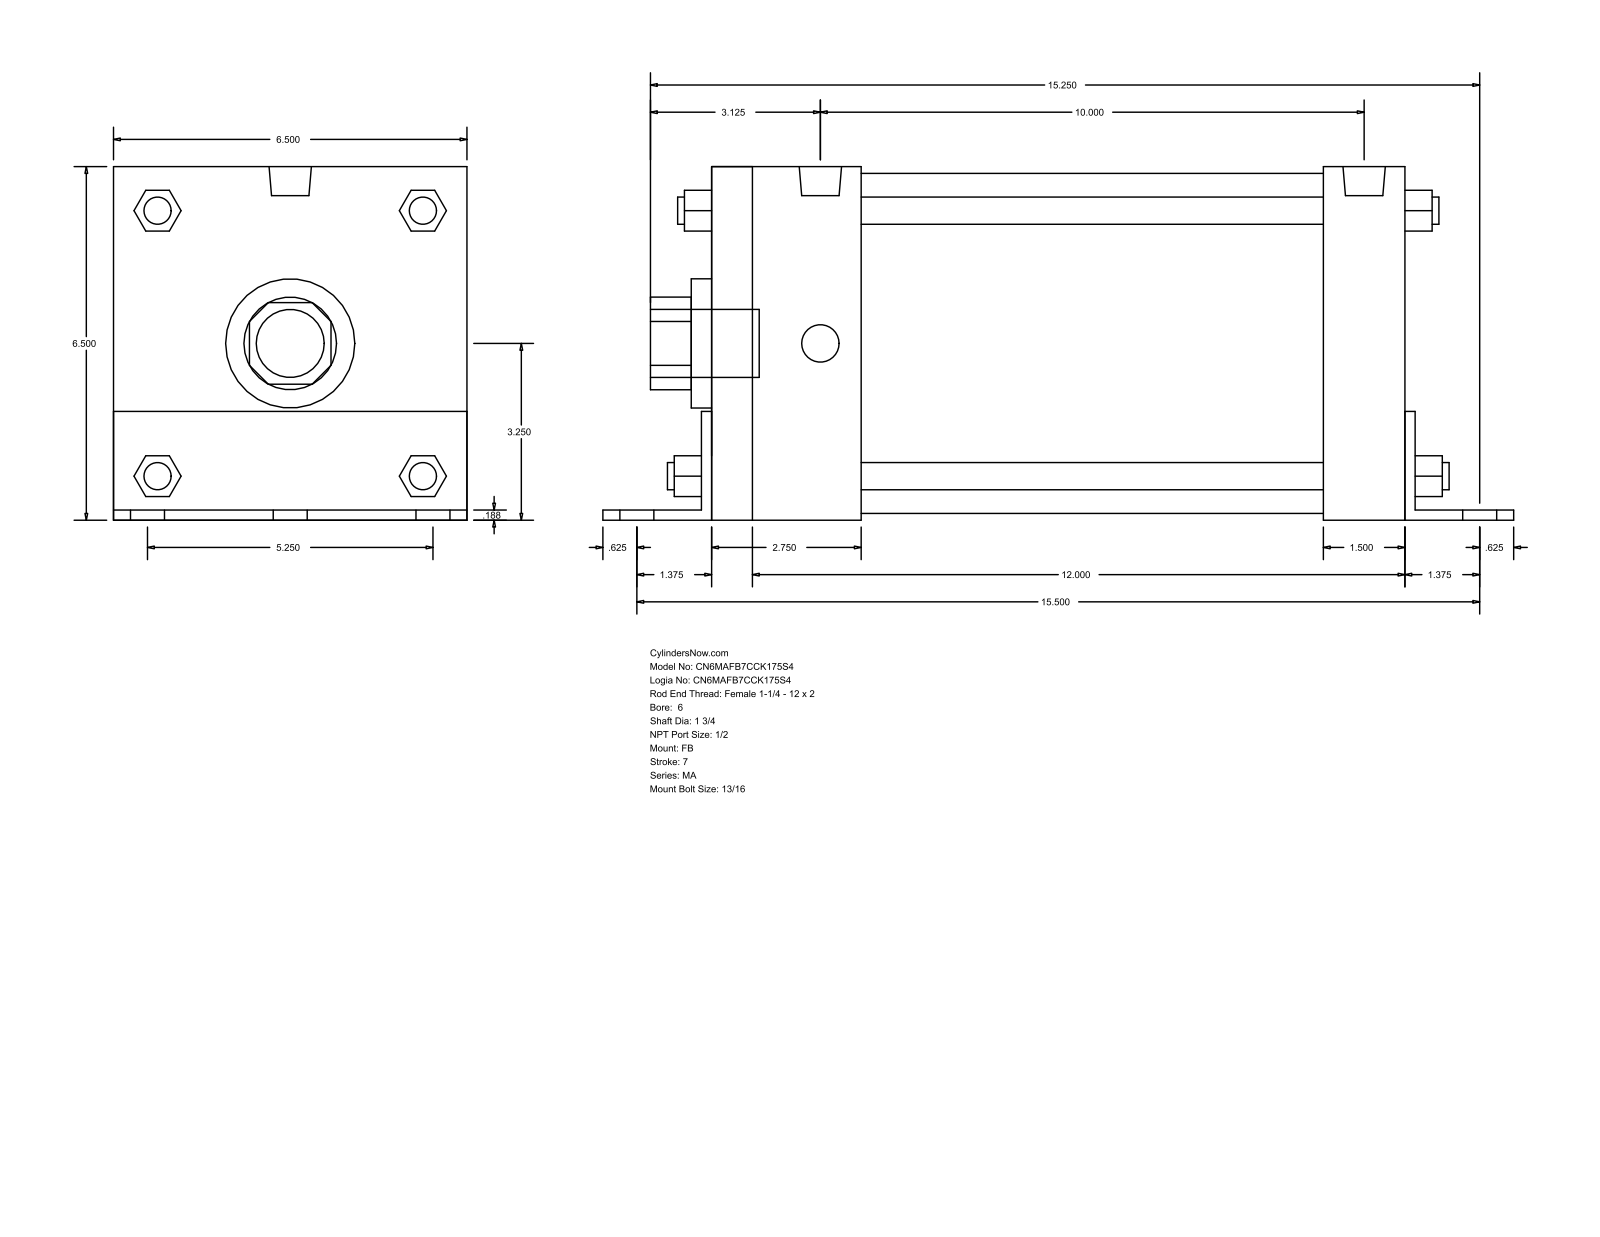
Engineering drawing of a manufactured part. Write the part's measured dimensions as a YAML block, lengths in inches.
part_name: "MA_FB__0600_1.75"
step_written_by: "GSSL Pune (CONFIG_CONTROL_DESIGN)"
units: inches
bodies: {solids: 0, faces: 140, planar: 105, cylindrical: 35, other: 0}
overall_size: [16.75, 6.502, 6.5]
round_holes:
  - {diameter: 1.75, count: 1}
  - {diameter: 2.375, count: 1}
  - {diameter: 6.25, count: 1}
round_bosses_or_shafts:
  - {diameter: 0.813, count: 6}
  - {diameter: 0.687, count: 4}
  - {diameter: 0.5, count: 4}
  - {diameter: 0.778, count: 2}
  - {diameter: 1.25, count: 1}
partial_cylinders:
  - {radius: 0.852, count: 1}
  - {radius: 1.262, count: 1}
face_to_face_distances: [6.5, 0.187, 12.75, 6.502, 12.938, 0.185, 6.315, 13.125, 1.5, 2.937]
